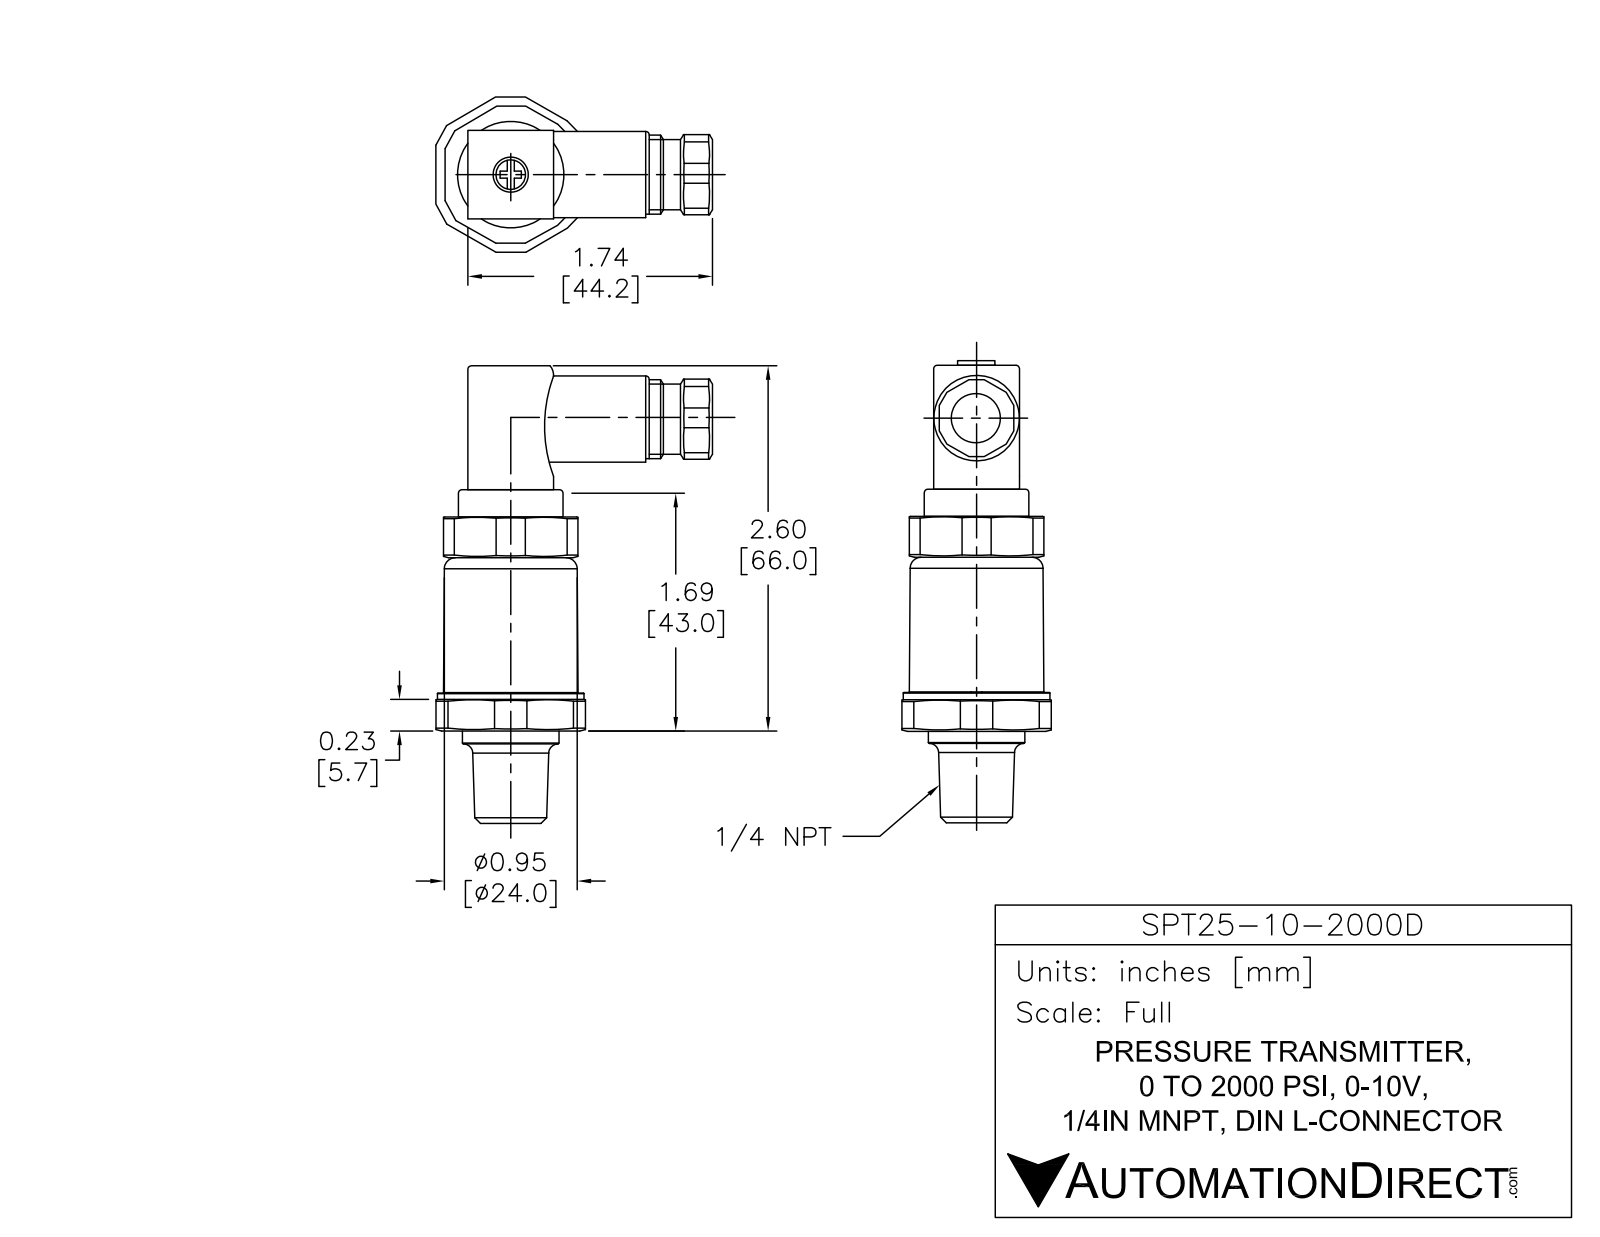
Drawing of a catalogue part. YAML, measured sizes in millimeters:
part_name: "SPT25-10-2000D"
step_written_by: "SolidWorks 2011 (AUTOMOTIVE_DESIGN)"
units: millimeters
bodies: {solids: 5, faces: 170, planar: 96, cylindrical: 64, other: 10}
overall_size: [81.25, 38.01, 35.71]
volume: 27900
surface_area: 10134
round_holes:
  - {diameter: 1, count: 1}
  - {diameter: 3.3, count: 1}
  - {diameter: 7, count: 1}
  - {diameter: 8, count: 1}
round_bosses_or_shafts:
  - {diameter: 26.75, count: 1}
  - {diameter: 24, count: 1}
  - {diameter: 17.5, count: 1}
  - {diameter: 15, count: 1}
  - {diameter: 14, count: 1}
  - {diameter: 11, count: 1}
partial_cylinders:
  - {radius: 1.5, count: 8}
  - {radius: 1.15, count: 4}
  - {radius: 2.25, count: 4}
  - {radius: 2, count: 3}
  - {radius: 1.15, count: 1}
  - {radius: 1.17, count: 1}
  - {radius: 14.5, count: 1}
face_to_face_distances: [1.5, 29.5, 31, 15.75, 0.35, 15.4, 6.75, 37.75, 36.25, 5]
hole_center_spacings: [1.33]
